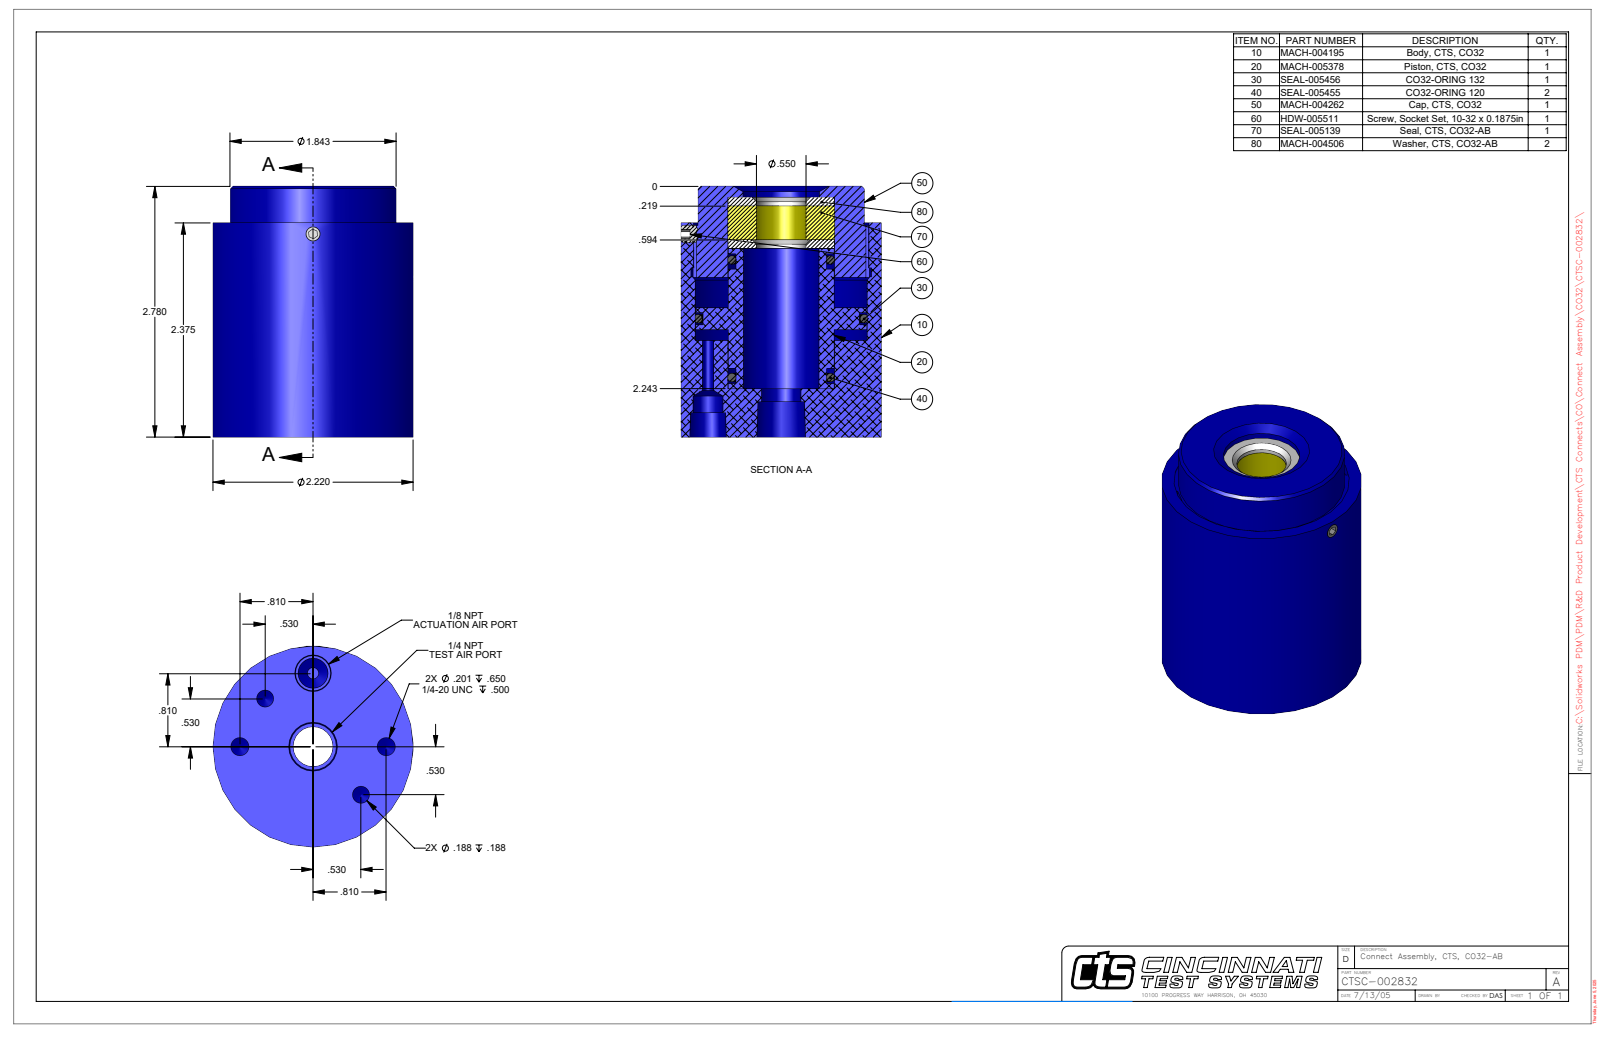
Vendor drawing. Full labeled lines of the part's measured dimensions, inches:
Part name (STEP PRODUCT): CTSC-002832
STEP written by: SolidWorks 2023 (AUTOMOTIVE_DESIGN)
Units: inches
Bodies: 1 solid, 124 faces (51 planar, 48 cylindrical, 25 other)
Overall size (bounding box): 2.78 × 2.22 × 2.22
Volume: 8.974 in³ · Surface area: 35.65 in²
Round holes (diameter × count): ⌀0.187 ×2, ⌀0.201 ×2, ⌀0.094 ×1, ⌀0.125 ×1, ⌀0.159 ×1, ⌀0.332 ×1, ⌀0.438 ×1, ⌀0.55 ×1, ⌀0.552 ×1, ⌀0.837 ×1, ⌀0.848 ×1, ⌀0.866 ×1
Round bosses / shafts (diameter × count): ⌀2.22 ×1, ⌀1.843 ×1, ⌀1.172 ×1
Partial cylindrical surfaces — rounded edges, fillets, slot ends (radius × count): R0.095 ×1, R1.094 ×1
Main face-to-face distances: 2.78, 2.375, 0.405, 0.537, 1.837, 2.243, 2.092, 1.554, 0.283, 0.688
Hole centre spacings: 0.6, 0.81, 1.441, 0.75, 1.145, 1.5, 1.62
